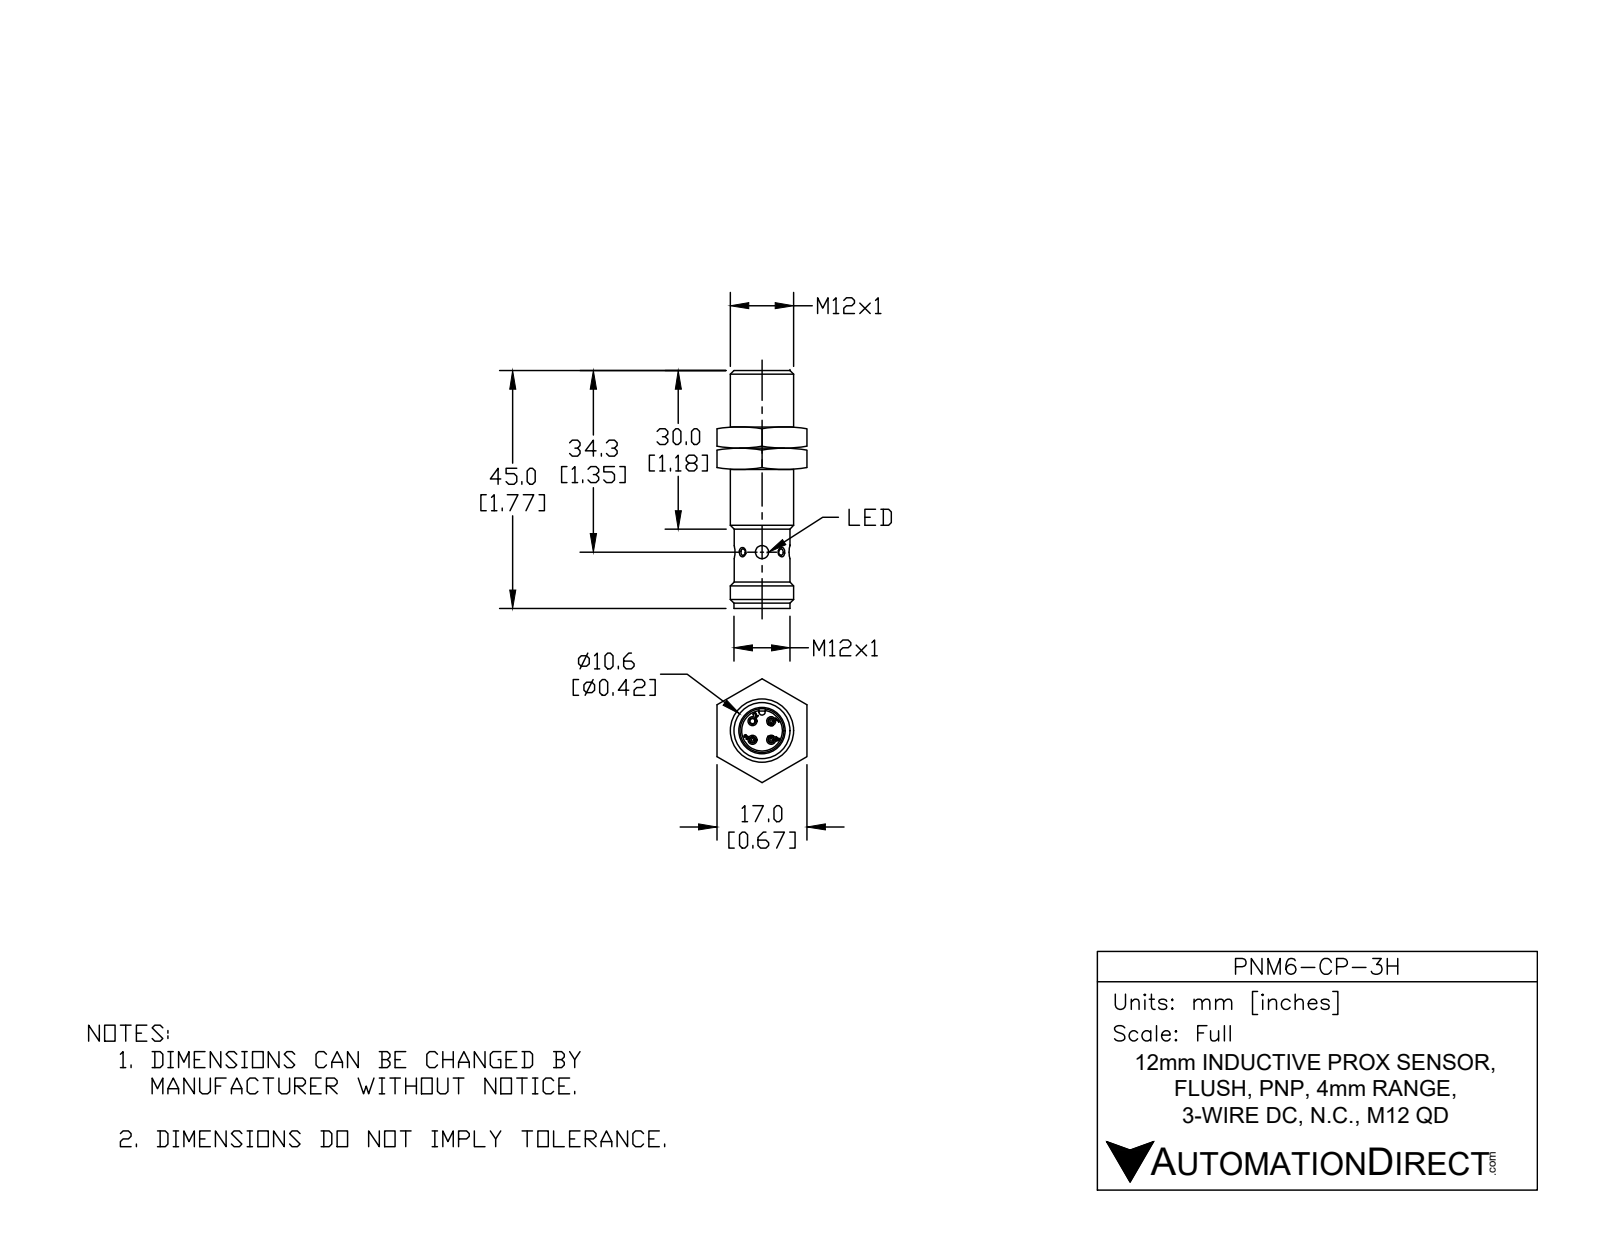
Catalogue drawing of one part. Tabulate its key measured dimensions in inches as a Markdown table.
| quantity | value |
| --- | --- |
| part name | PNM6-CP-3H |
| STEP written by | SolidWorks 2017 (AUTOMOTIVE_DESIGN) |
| units | inches |
| bodies | 1 solid, 491 faces (117 planar, 138 cylindrical, 236 other) |
| overall size | 1.772 × 0.472 × 0.472 |
| volume | 0.247 in³ |
| surface area | 8.016 in² |
| round holes (diameter × count) | 0.043 × 3, 0.04 × 2, 0.098 × 2, 0.038 × 1, 0.04 × 1, 0.327 × 1, 0.394 × 1, 0.401 × 1 |
| round bosses / shafts (diameter × count) | 0.039 × 6, 0.472 × 1, 0.417 × 1, 0.415 × 1, 0.4 × 1, 0.392 × 1, 0.39 × 1, 0.38 × 1 |
| partial cylindrical surfaces (radius × count) | 0.004 × 36, 0.079 × 6, 0.024 × 1, 0.031 × 1, 0.161 × 1 |
| main face-to-face distances | 0.118, 1.299, 1.181, 0.018, 0.1, 1.281, 1.303, 1.421, 1.404, 0.122 |
| hole center spacings | 0.098, 0.139, 0.197 |
